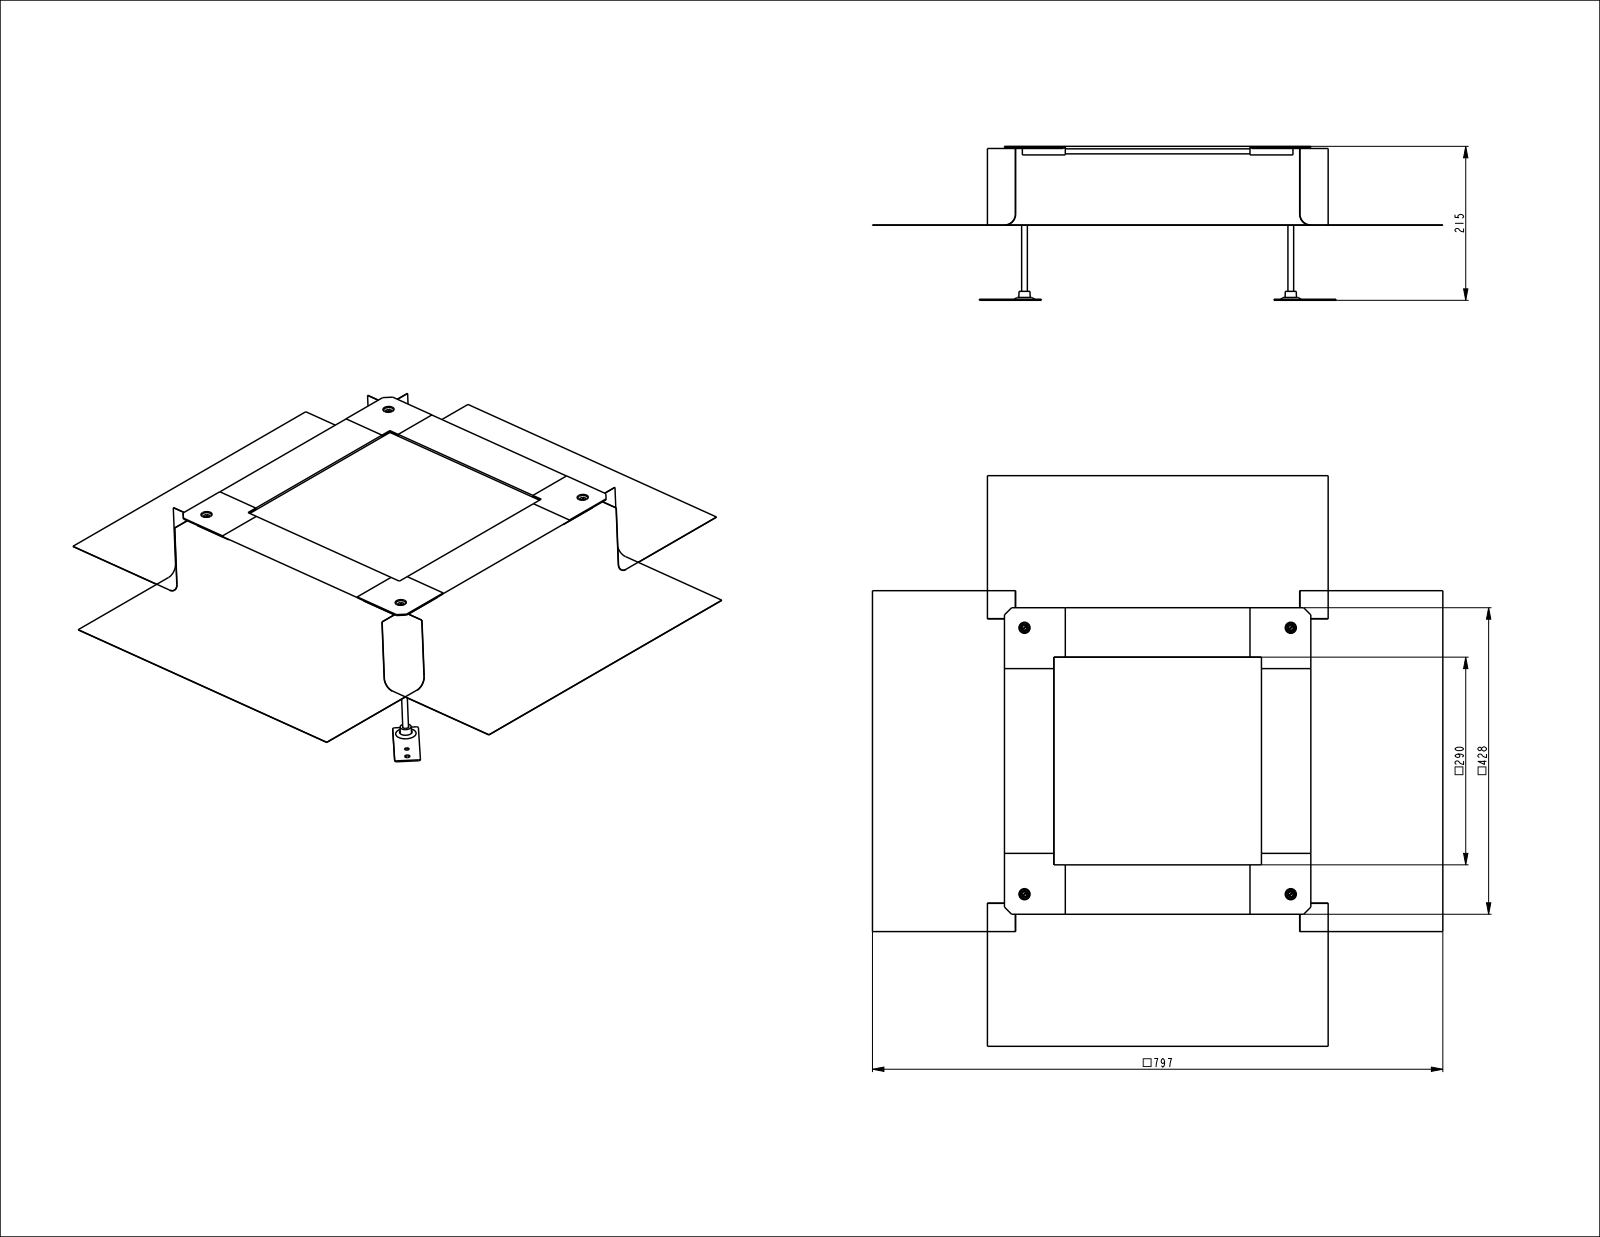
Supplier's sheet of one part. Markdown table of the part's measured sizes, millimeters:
| quantity | value |
| --- | --- |
| part name | U05347KUN; U05349KUN; U05829KUN_ASM; U09125KUN (+6 more) |
| STEP written by | CREO PARAMETRIC BY PTC INC, 2020281 (CONFIG_CONTROL_DESIGN) |
| units | millimeters |
| bodies | 25 solids, 930 faces (578 planar, 240 cylindrical, 112 other) |
| overall size | 900.29 × 900.01 × 215 |
| volume | 938 337 mm³ |
| surface area | 1 705 000 mm² |
| round holes (diameter × count) | 6 × 4, 6.6 × 4, 7 × 4, 8.5 × 4, 11.5 × 4, 17.5 × 4, 23 × 4 |
| round bosses / shafts (diameter × count) | 8 × 6, 20 × 4 |
| partial cylindrical surfaces (radius × count) | 0.25 × 32, 3 × 16, 0.7 × 12, 1.47 × 12, 0.52 × 8, 17.6 × 8, 0.28 × 4, 0.41 × 4 |
| main face-to-face distances | 0.4, 397.14, 4, 3, 1, 110.15, 109.75, 107.15, 106.75, 106.15 |
| hole center spacings | 402.8, 418.15, 445.77, 20, 42, 62, 372, 568.09 |
